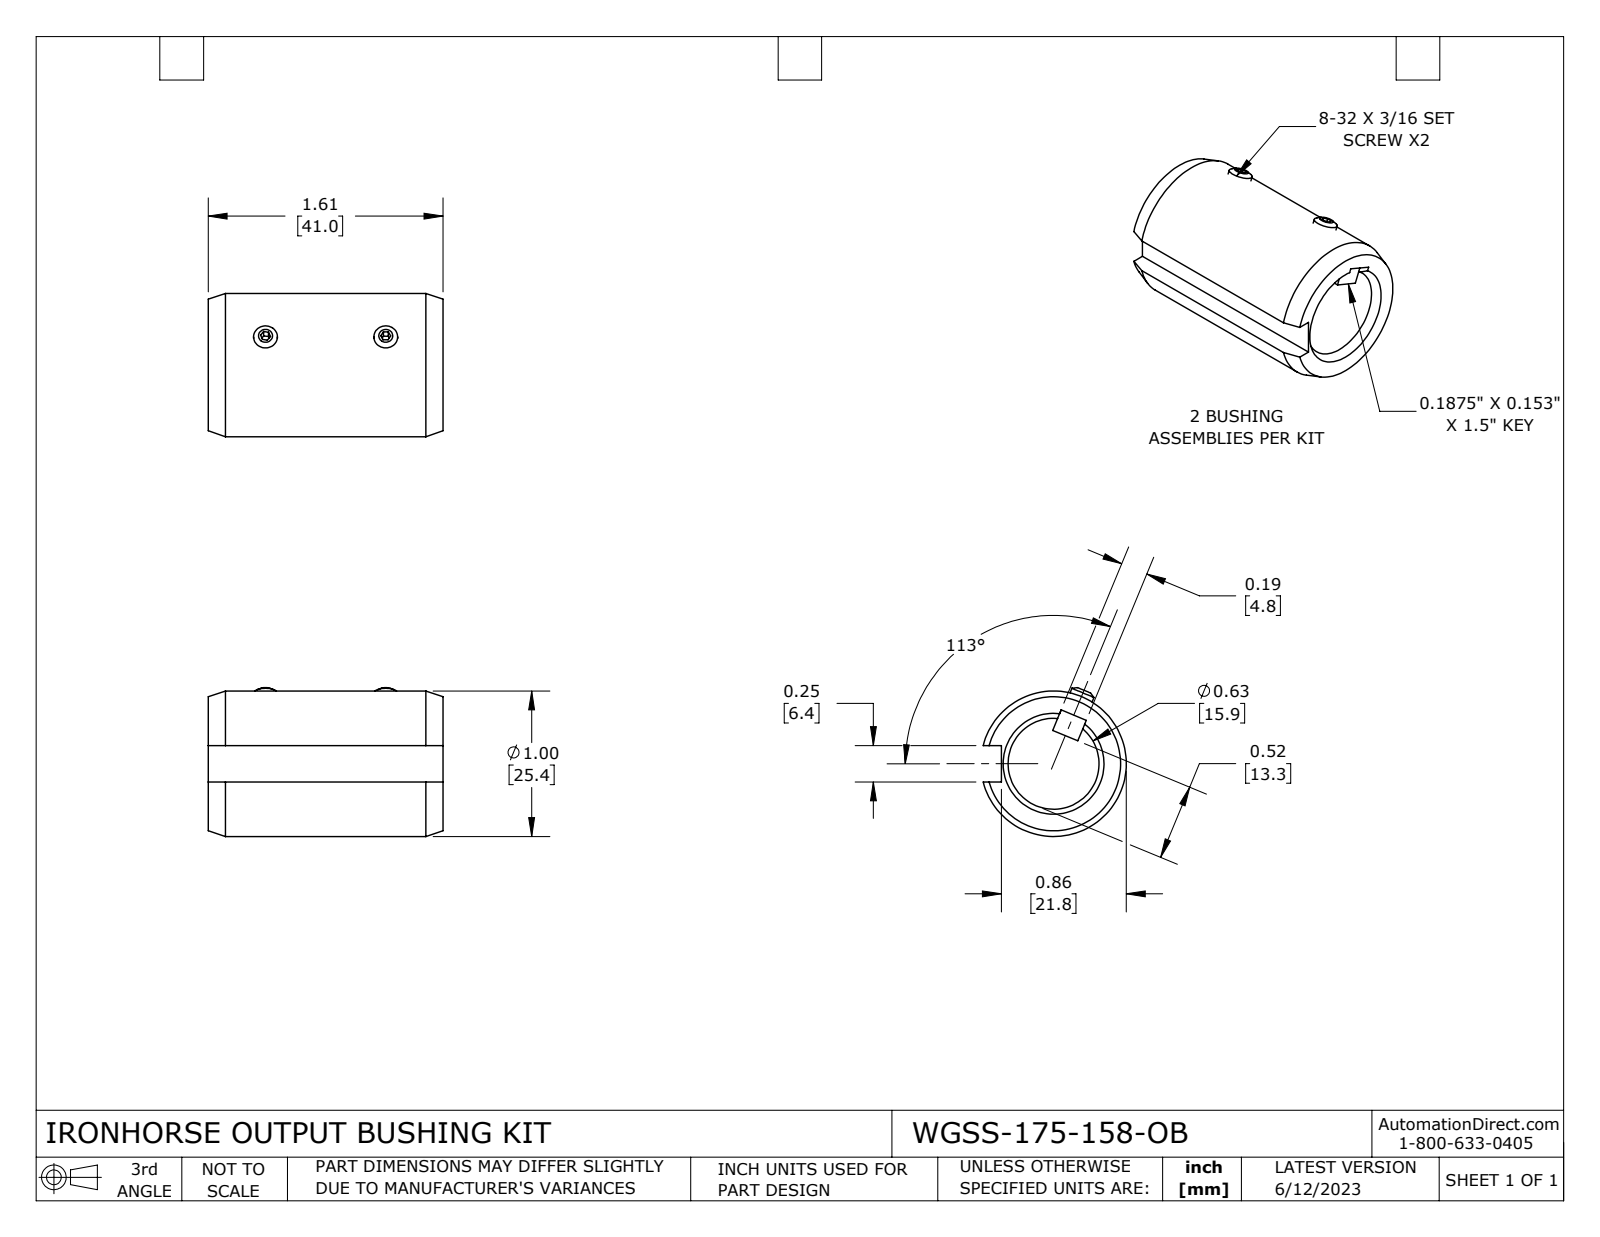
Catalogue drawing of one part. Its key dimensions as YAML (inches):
part_name: "WGSS-175-158-OB"
step_written_by: "SolidWorks 2021 (CONFIG_CONTROL_DESIGN)"
units: inches
bodies: {solids: 4, faces: 66, planar: 32, cylindrical: 14, other: 20}
overall_size: [1.614, 1.024, 0.984]
volume: 0.73
surface_area: 10.81
round_holes:
  - {diameter: 0.136, count: 2}
  - {diameter: 0.625, count: 1}
round_bosses_or_shafts:
  - {diameter: 0.164, count: 2}
  - {diameter: 1, count: 1}
face_to_face_distances: [0.187, 0.153, 0.153, 1.614, 0.25, 0.043, 1.571, 1.543, 1.5, 0.071]
hole_center_spacings: [0.827]
